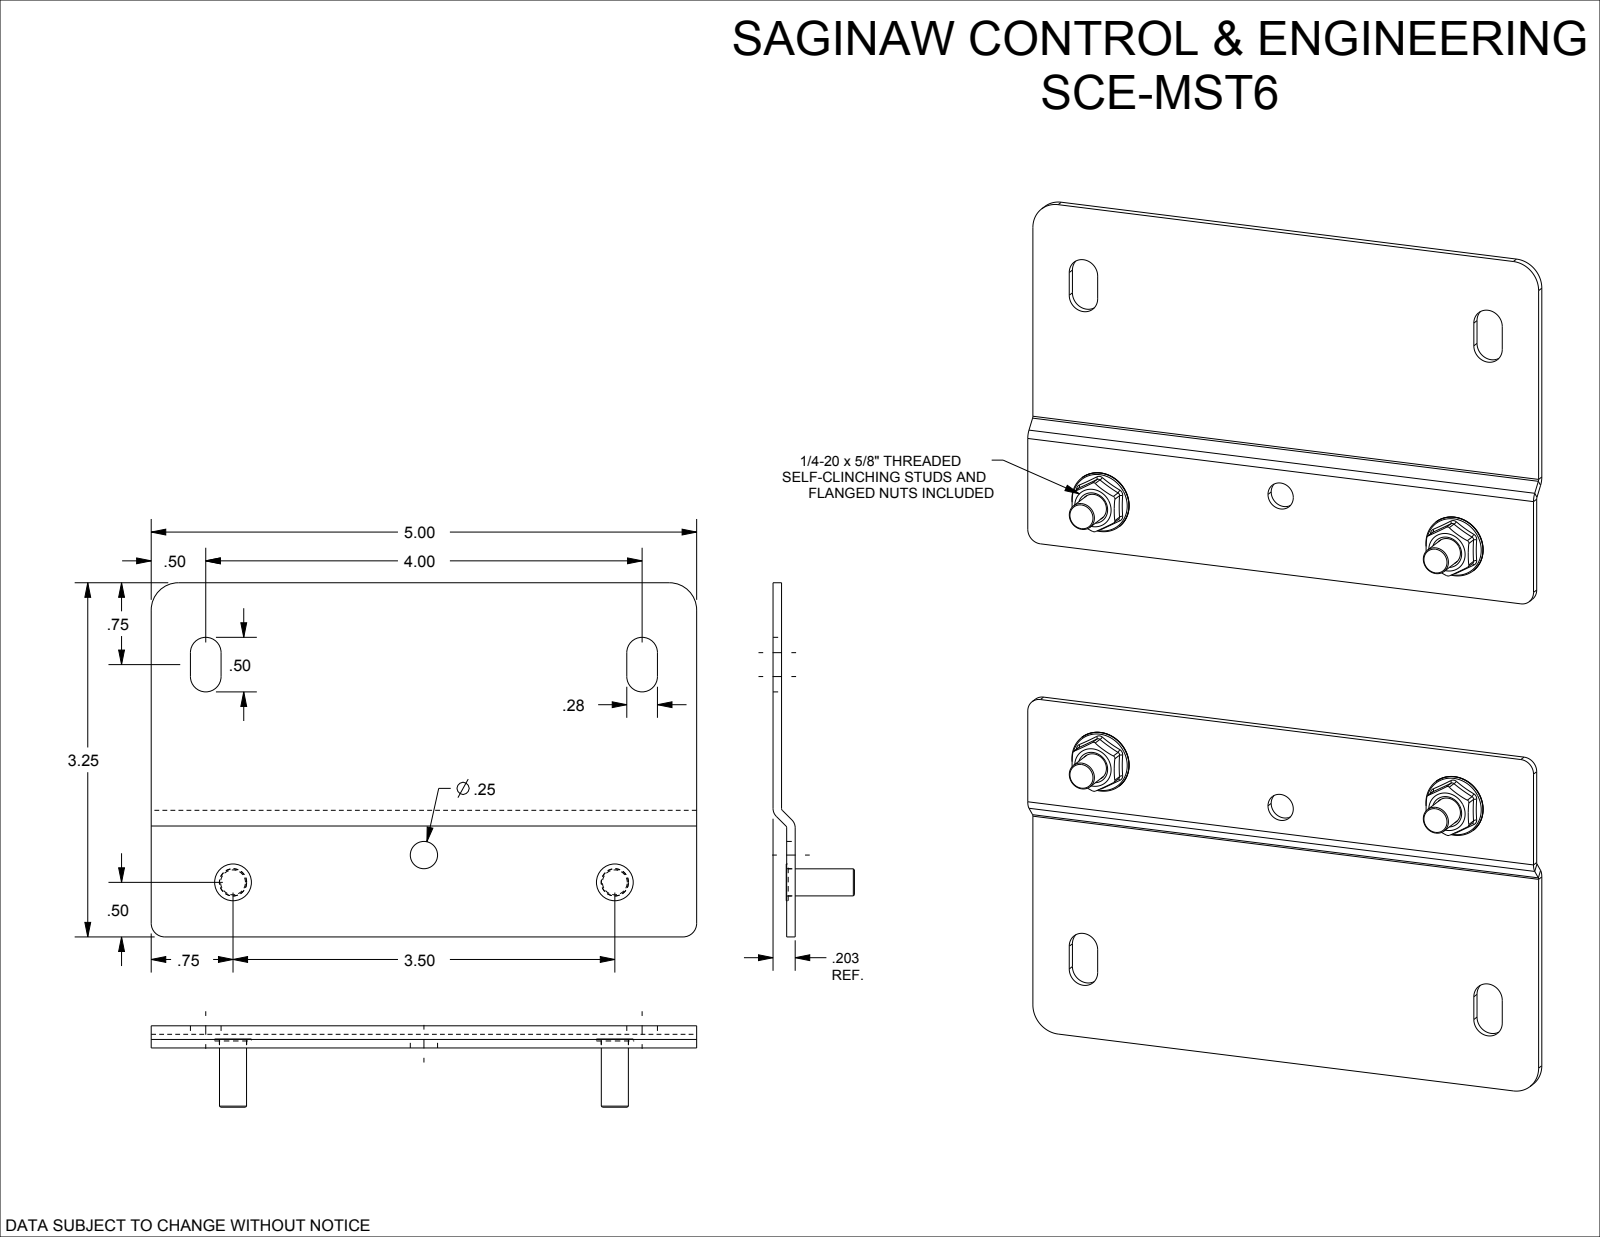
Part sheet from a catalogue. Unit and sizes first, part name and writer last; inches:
Units: inches
Overall size (bounding box): 7.99 × 5 × 0.746
Round holes (diameter × count): ⌀0.25 ×6, ⌀0.25 ×4
Round bosses / shafts (diameter × count): ⌀0.563 ×4, ⌀0.337 ×4, ⌀0.248 ×4
Partial cylindrical surfaces — rounded edges, fillets, slot ends (radius × count): R0.029 ×24, R0.141 ×8, R0.023 ×4, R0.101 ×4, R0.125 ×4, R0.25 ×4
Main face-to-face distances: 0.078, 0.078, 0.203, 0.125, 0.047, 0.125, 3.245, 4.745, 5, 1.5
Hole centre spacings: 1.768, 3.259, 2.5, 3.5, 4.301, 3
Volume: 2.708 in³ · Surface area: 73.06 in²
Bodies: 10 solids, 1010 faces (332 planar, 70 cylindrical, 608 other)
Part name (STEP PRODUCT): SCE-MST6
STEP written by: SolidWorks 2019 (AUTOMOTIVE_DESIGN)
